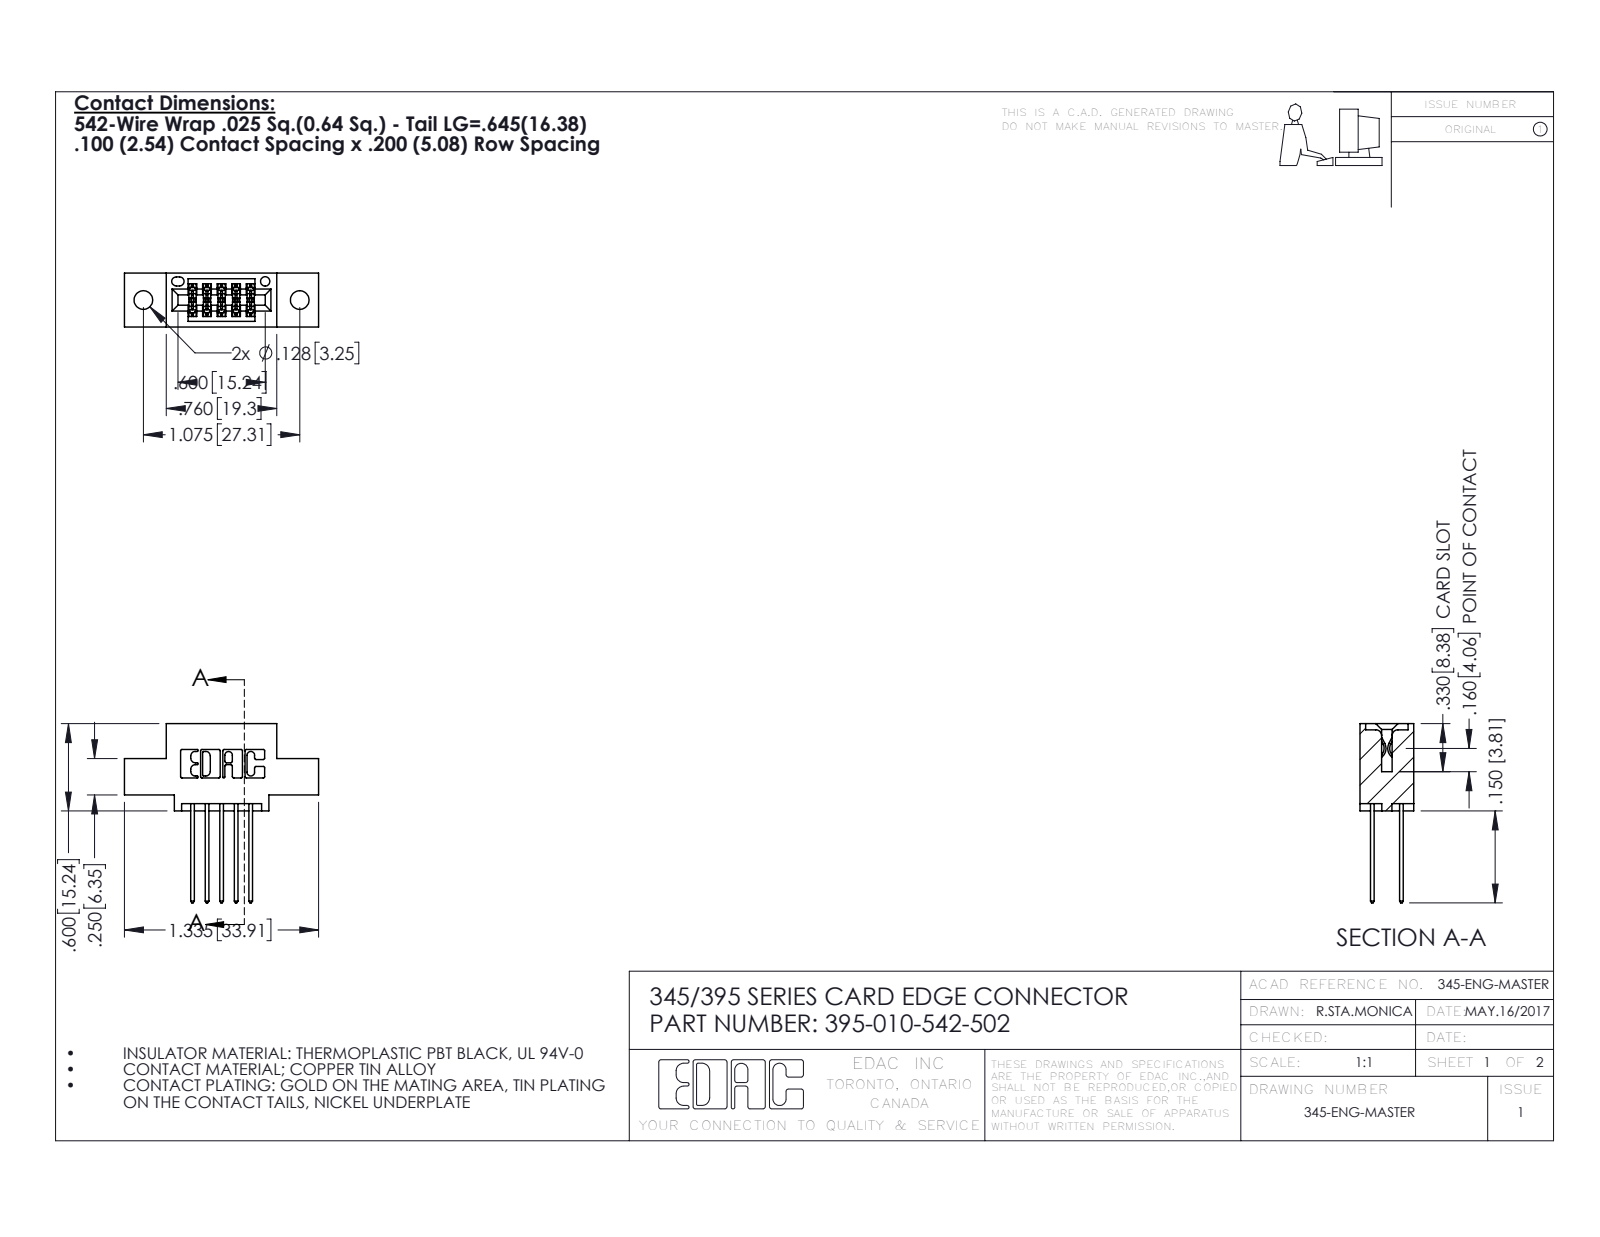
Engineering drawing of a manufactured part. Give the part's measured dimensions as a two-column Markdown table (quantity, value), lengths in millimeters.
| quantity | value |
| --- | --- |
| part name | 395-010-542-502; 345 Part_0.110 Offset - 0.128 Dia; 345-292-001_345-293-142 |
| STEP written by | SolidWorks 2016 (CONFIG_CONTROL_DESIGN) |
| units | millimeters |
| bodies | 11 solids, 630 faces (414 planar, 216 cylindrical, 0 other) |
| overall size | 33.9 × 31.3 × 9.4 |
| volume | 2 880 mm³ |
| surface area | 3 589 mm² |
| round holes (diameter × count) | 3.3 × 2, 1.6 × 1 |
| partial cylindrical surfaces (radius × count) | 0.3 × 22, 0.2 × 15, 0.3 × 10, 0.2 × 6, 0.8 × 6, 0.7 × 3, 0.4 × 2, 0.5 × 2 |
| main face-to-face distances | 5.1, 7.6, 1.8, 9.4, 2.5, 2.5, 6.9, 0.6, 5.7, 6.4 |
| hole center spacings | 6.9, 21.5, 27.3 |
